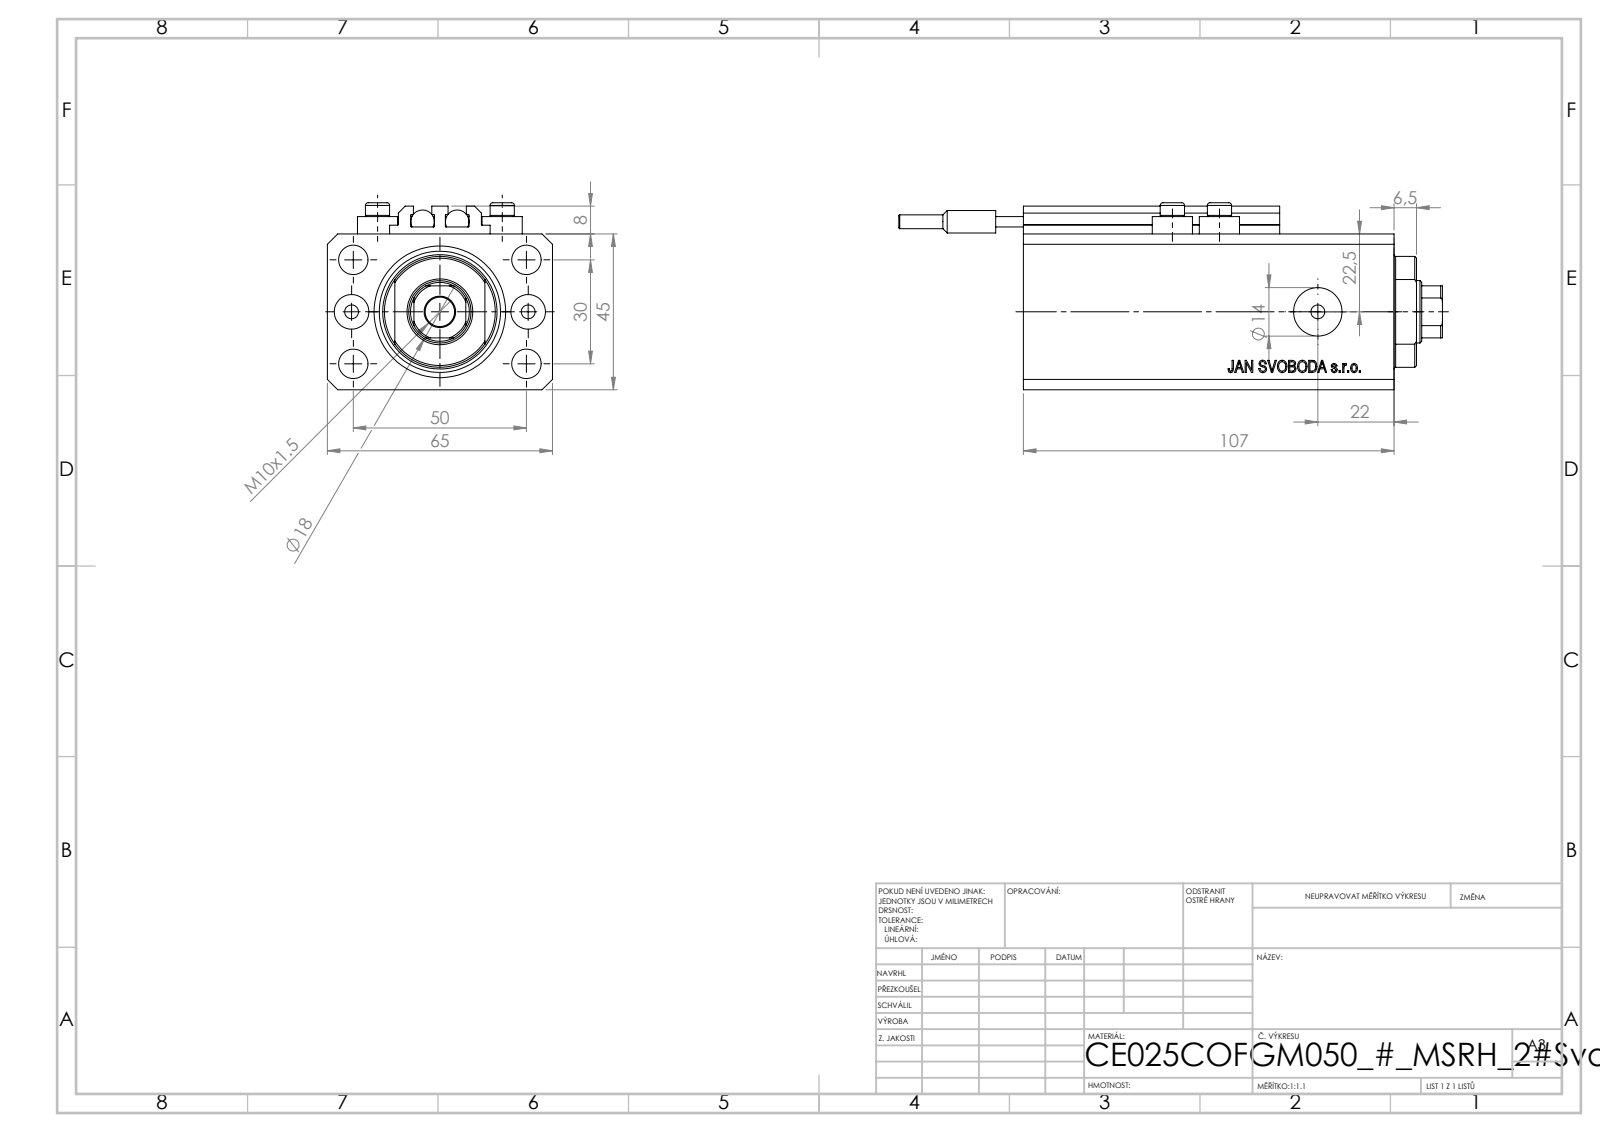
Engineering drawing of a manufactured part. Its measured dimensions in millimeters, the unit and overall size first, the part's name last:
Units: millimetres
Overall size (bounding box): 157 × 65 × 54
Round holes (diameter × count): ⌀4 ×8, ⌀8.5 ×5, ⌀10 ×2, ⌀14 ×2, ⌀18 ×1, ⌀25 ×1, ⌀38 ×1
Round bosses / shafts (diameter × count): ⌀11.6 ×4, ⌀7 ×4, ⌀6.8 ×2, ⌀6.5 ×2, ⌀4 ×2
Partial cylindrical surfaces — rounded edges, fillets, slot ends (radius × count): R0.2 ×10, R8.5 ×1, R16 ×1
Main face-to-face distances: 45, 65, 14, 47, 93, 107, 3, 2, 10, 2.5
Hole centre spacings: 15.01, 29.15, 52.68, 13.6, 25.5, 30, 36, 38.48
Volume: 292 606 mm³ · Surface area: 76 686 mm²
Bodies: 10 solids, 1086 faces (536 planar, 98 cylindrical, 452 other)
Part name (STEP PRODUCT): V250CE_VC_C; ALLEN BOLT V250CE; V250CE_C_VCP; V250CE_C_Body (+1 more)
STEP written by: SolidWorks 2019 (CONFIG_CONTROL_DESIGN)
